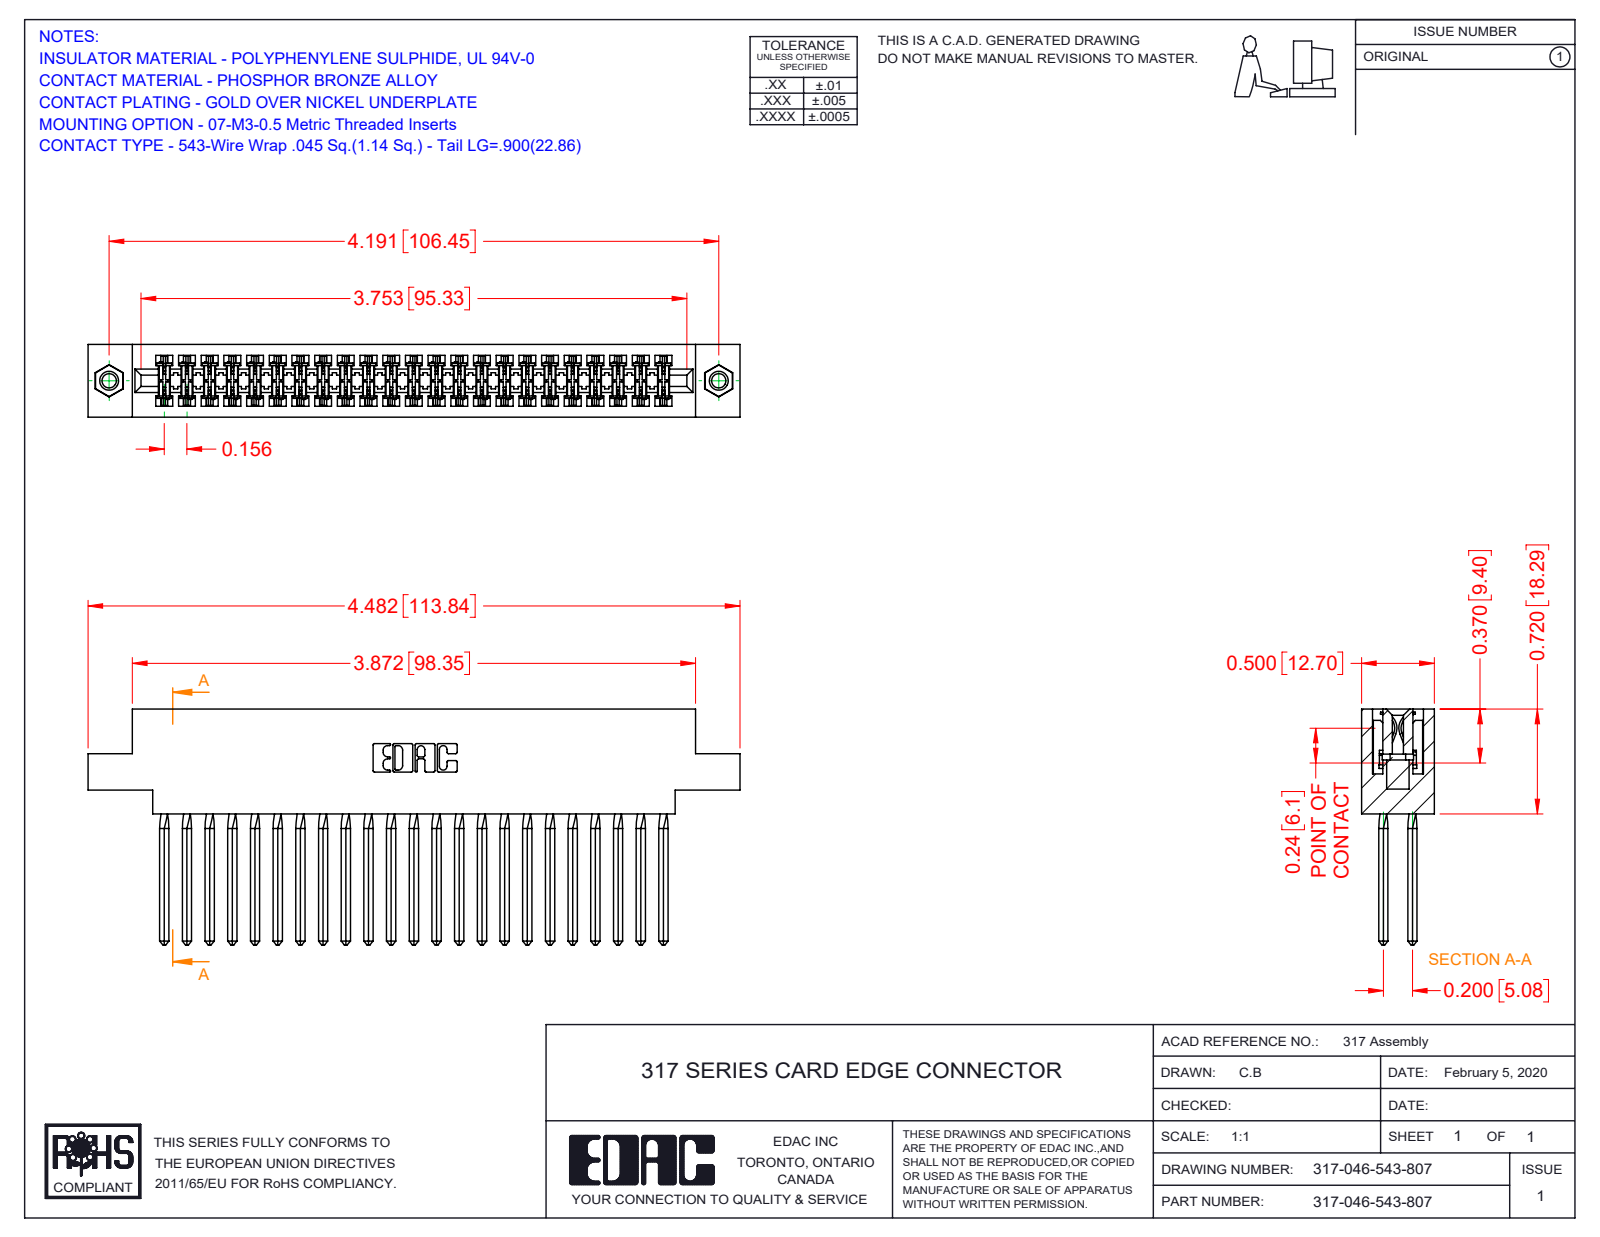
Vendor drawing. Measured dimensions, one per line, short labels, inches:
name: 317-046-543-807; 345-250-001_345-250-005-103; 317-290-001_543; 317 Part_.156 Dia - TI
written by: SolidWorks 2016 (CONFIG_CONTROL_DESIGN)
unit: in
bodies: 49 solids, 4256 faces (3448 planar, 608 cylindrical, 200 other)
size: 4.482 × 1.62 × 0.5
volume: 1.14 in³; area: 42.82 in²
holes: 2× ⌀0.098, 2× ⌀0.125, 2× ⌀0.156
bosses: 2× ⌀0.155
rounds: 92× R0.015, 22× R0.01, 6× R0.007, 6× R0.031, 3× R0.026, 2× R0.095, 2× R0.1, 2× R0.11
face distances: 0.5, 0.075, 0.425, 0.11, 0.35, 0.195, 0.22, 0.094, 0.72, 0.2
hole spacings: 4.191
